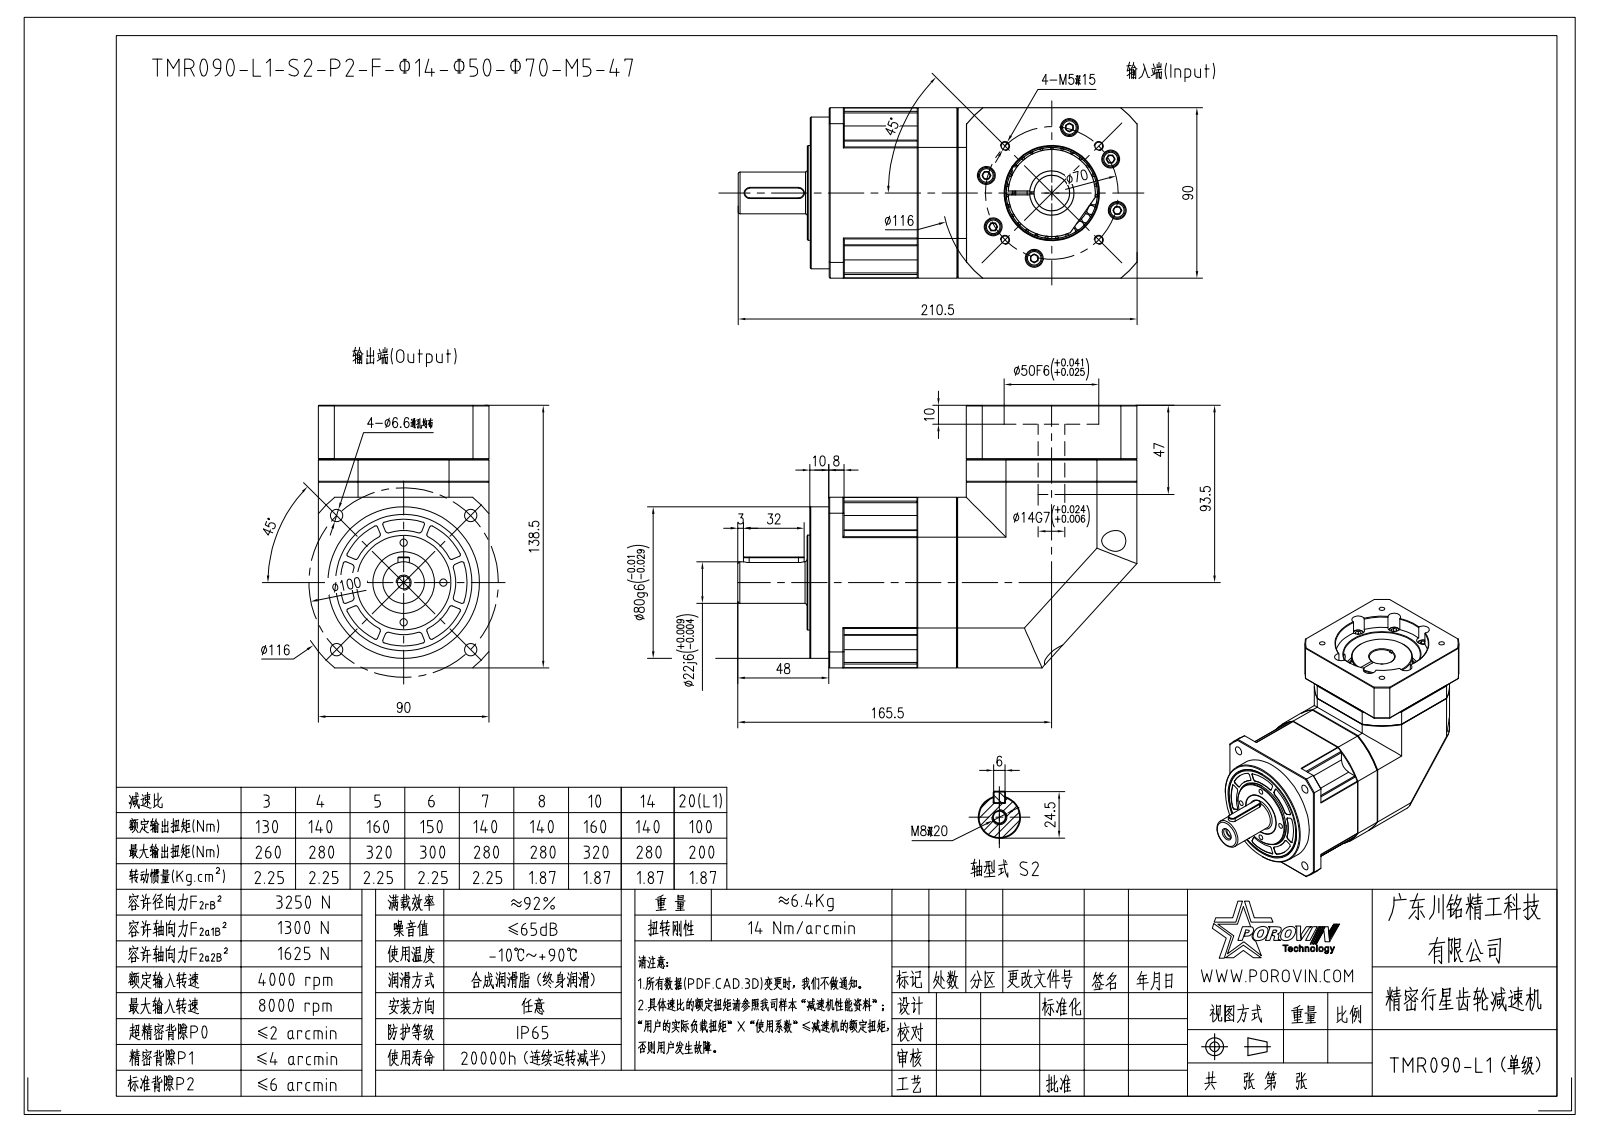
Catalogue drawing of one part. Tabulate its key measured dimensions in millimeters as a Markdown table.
| quantity | value |
| --- | --- |
| part name | HEXAGON_SOCKET_HEAD_CAP_S-14521; SPRING_LOCK_WASHERS--NORM-14468; HEXAGON_SOCKET_HEAD_CAP_SC-3768; HEXAGON_SOCKET_HEAD_CAP_S-14563 (+8 more) |
| STEP written by | CREO PARAMETRIC BY PTC INC, 2020053 (CONFIG_CONTROL_DESIGN) |
| units | millimeters |
| bodies | 43 solids, 1285 faces (516 planar, 543 cylindrical, 226 other) |
| overall size | 210.5 × 138.5 × 90 |
| volume | 1 364 000 mm³ |
| surface area | 214 421 mm² |
| round holes (diameter × count) | 5.4 × 12, 5.5 × 12, 9.5 × 12, 4.2 × 11, 6.5 × 5, 4 × 4, 6.6 × 4, 6.68 × 4, 11 × 4, 50 × 2, 5 × 1, 6.8 × 1 |
| round bosses / shafts (diameter × count) | 8.5 × 12, 8 × 12, 5 × 12, 10 × 4, 9.88 × 4, 6 × 4, 80 × 1, 78 × 1 |
| partial cylindrical surfaces (radius × count) | 1 × 92, 7.5 × 4, 51 × 3, 3 × 2, 58 × 2, 4 × 1, 5.25 × 1, 40 × 1 |
| main face-to-face distances | 90, 12, 21.3, 21.5, 28.5, 26, 10, 110, 2.5, 31.3 |
| hole center spacings | 35.75, 27.36, 38.16, 66.06, 66.53, 56.13, 9.26, 43.08 |
